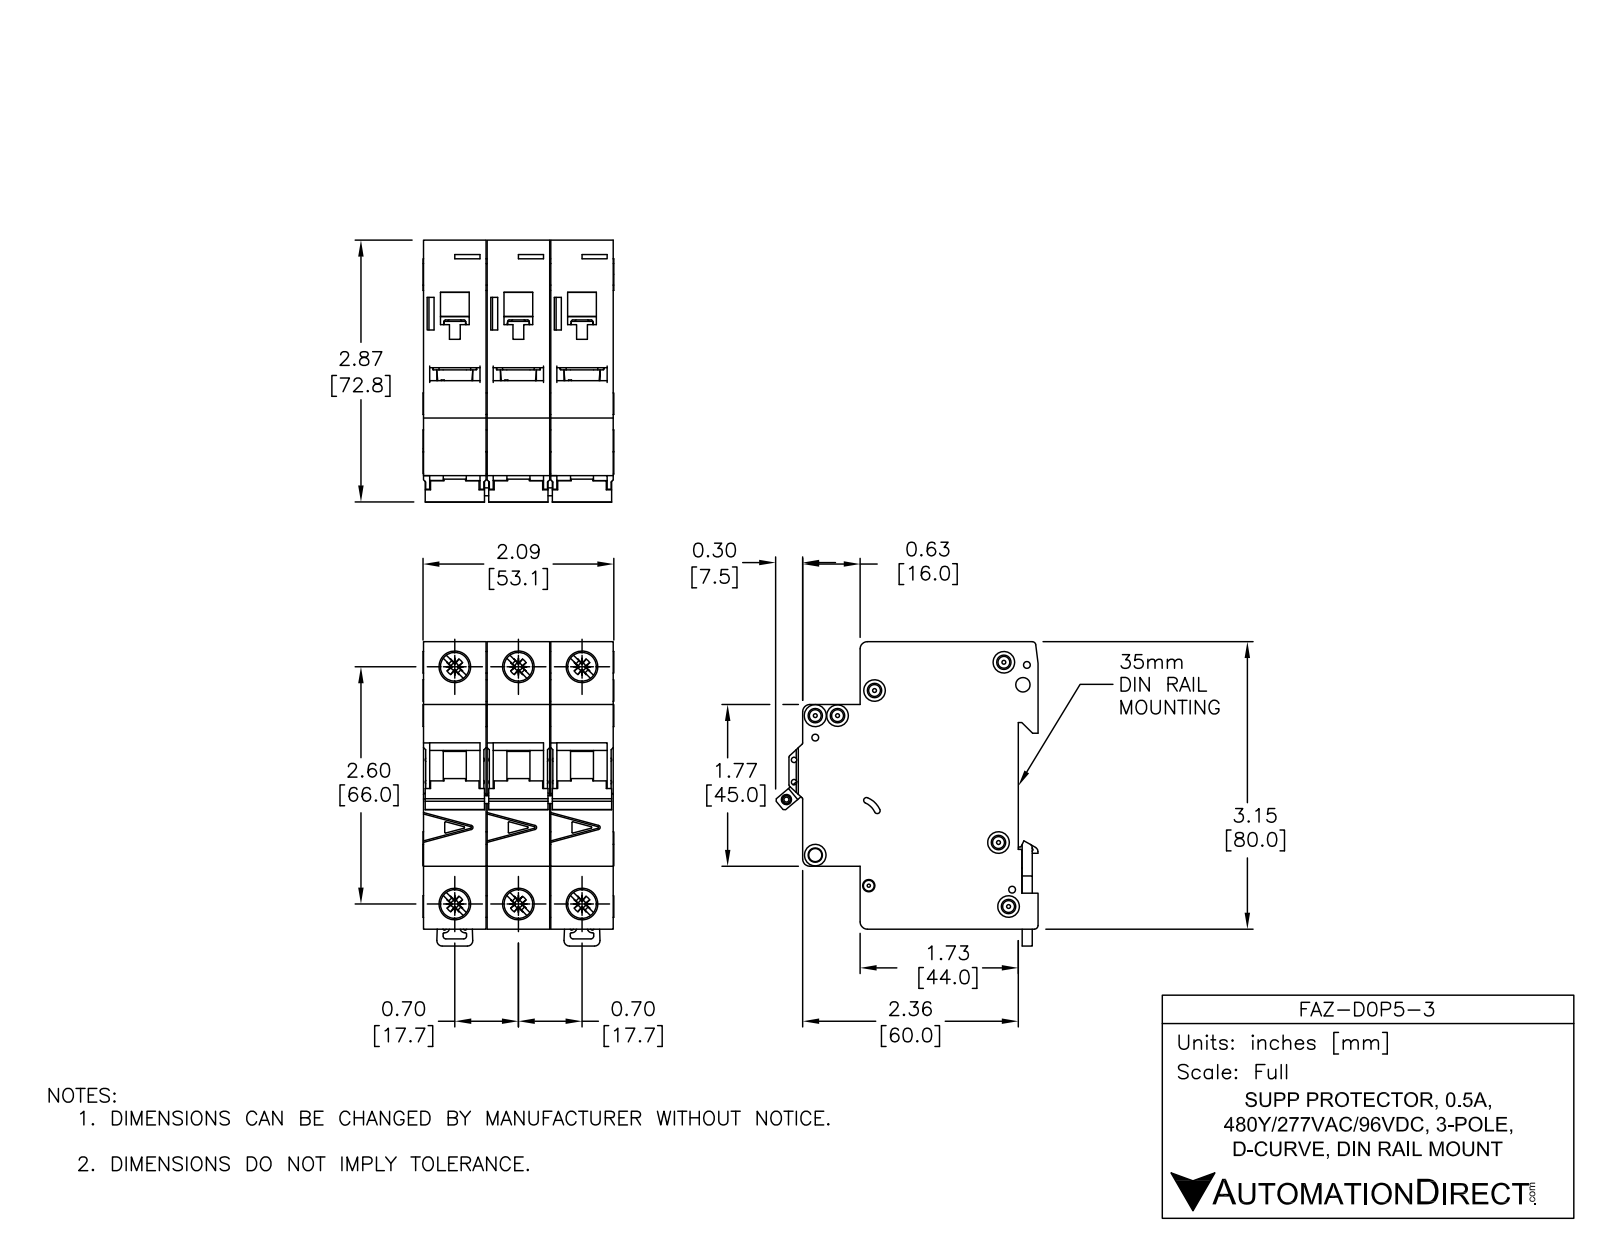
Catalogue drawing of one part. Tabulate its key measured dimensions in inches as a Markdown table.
| quantity | value |
| --- | --- |
| part name | FAZ-D0P5-3 |
| STEP written by | SolidWorks 2014 (AUTOMOTIVE_DESIGN) |
| units | inches |
| bodies | 11 solids, 1650 faces (697 planar, 590 cylindrical, 363 other) |
| overall size | 3.338 × 2.876 × 2.091 |
| volume | 13.71 in³ |
| surface area | 89.98 in² |
| round holes (diameter × count) | 0.142 × 6, 0.323 × 4, 0.075 × 3, 0.043 × 2, 0.059 × 2, 0.157 × 2, 0.281 × 2, 0.085 × 1, 0.087 × 1, 0.1 × 1, 0.13 × 1, 0.134 × 1 |
| round bosses / shafts (diameter × count) | 0.236 × 4, 0.098 × 3, 0.323 × 2 |
| partial cylindrical surfaces (radius × count) | 0.01 × 68, 0.02 × 25, 0.039 × 12, 0.079 × 12, 0.008 × 11, 0.071 × 3, 0.031 × 2, 0.118 × 2 |
| main face-to-face distances | 0.697, 0.689, 1.394, 1.386, 2.083, 0.705, 3.129, 0.217, 1.949, 1.732 |
| hole center spacings | 0.697, 2.69, 2.598, 0.244, 0.537, 1.394, 2.948, 0.189 |
